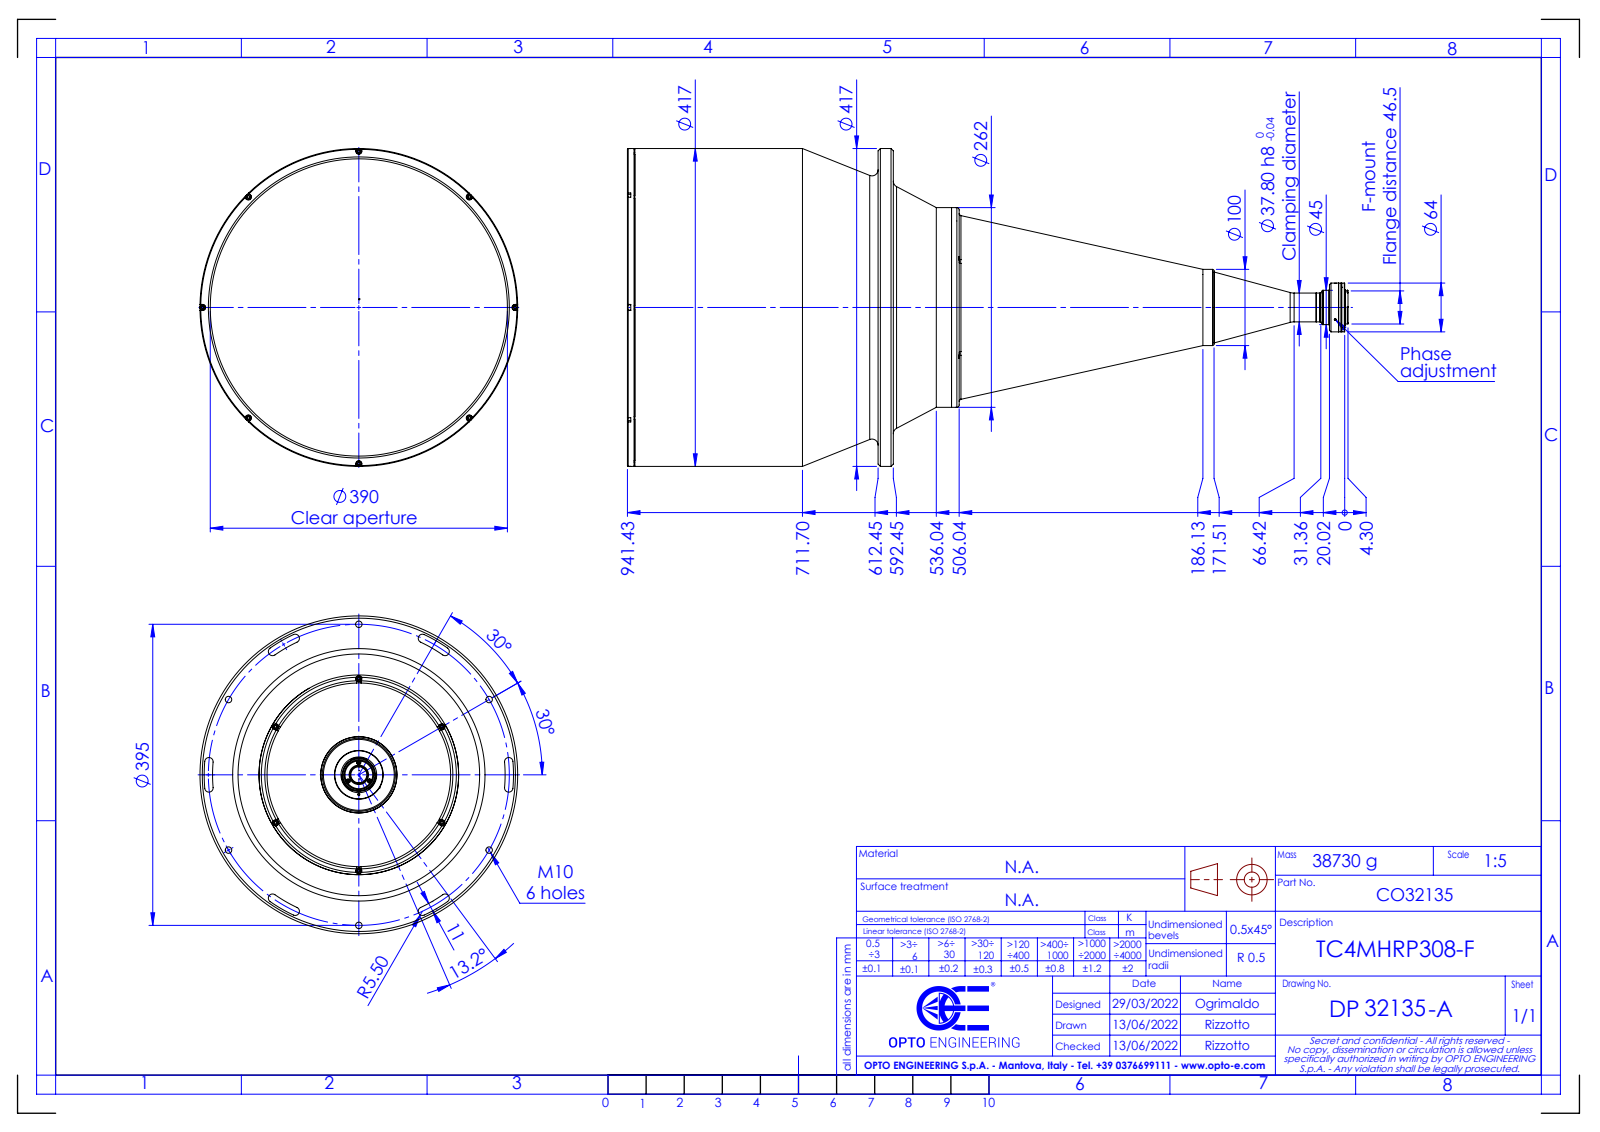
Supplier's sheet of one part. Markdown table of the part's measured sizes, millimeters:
| quantity | value |
| --- | --- |
| part name | DP32135-A_TC4MHRP308-F |
| STEP written by | SolidWorks 2021 (CONFIG_CONTROL_DESIGN) |
| units | millimeters |
| bodies | 0 solids, 308 faces (73 planar, 142 cylindrical, 93 other) |
| overall size | 945.73 × 417 × 417 |
| round holes (diameter × count) | 8 × 6, 8.5 × 6, 2.5 × 3, 42 × 1, 390 × 1 |
| round bosses / shafts (diameter × count) | 7 × 12, 5.5 × 2, 417 × 1, 262 × 1, 100 × 1, 93 × 1, 64 × 1, 63.5 × 1 |
| partial cylindrical surfaces (radius × count) | 5.5 × 12, 4 × 4, 1.15 × 2, 0.5 × 1, 22.65 × 1, 192 × 1, 203 × 1 |
| main face-to-face distances | 20, 96.41, 76.41, 328.98, 348.98, 425.39, 8.7, 320.28, 340.28, 416.69 |
| hole center spacings | 126, 173.2, 197.5, 282.43, 71.5, 218.24, 323.5, 342.08 |
